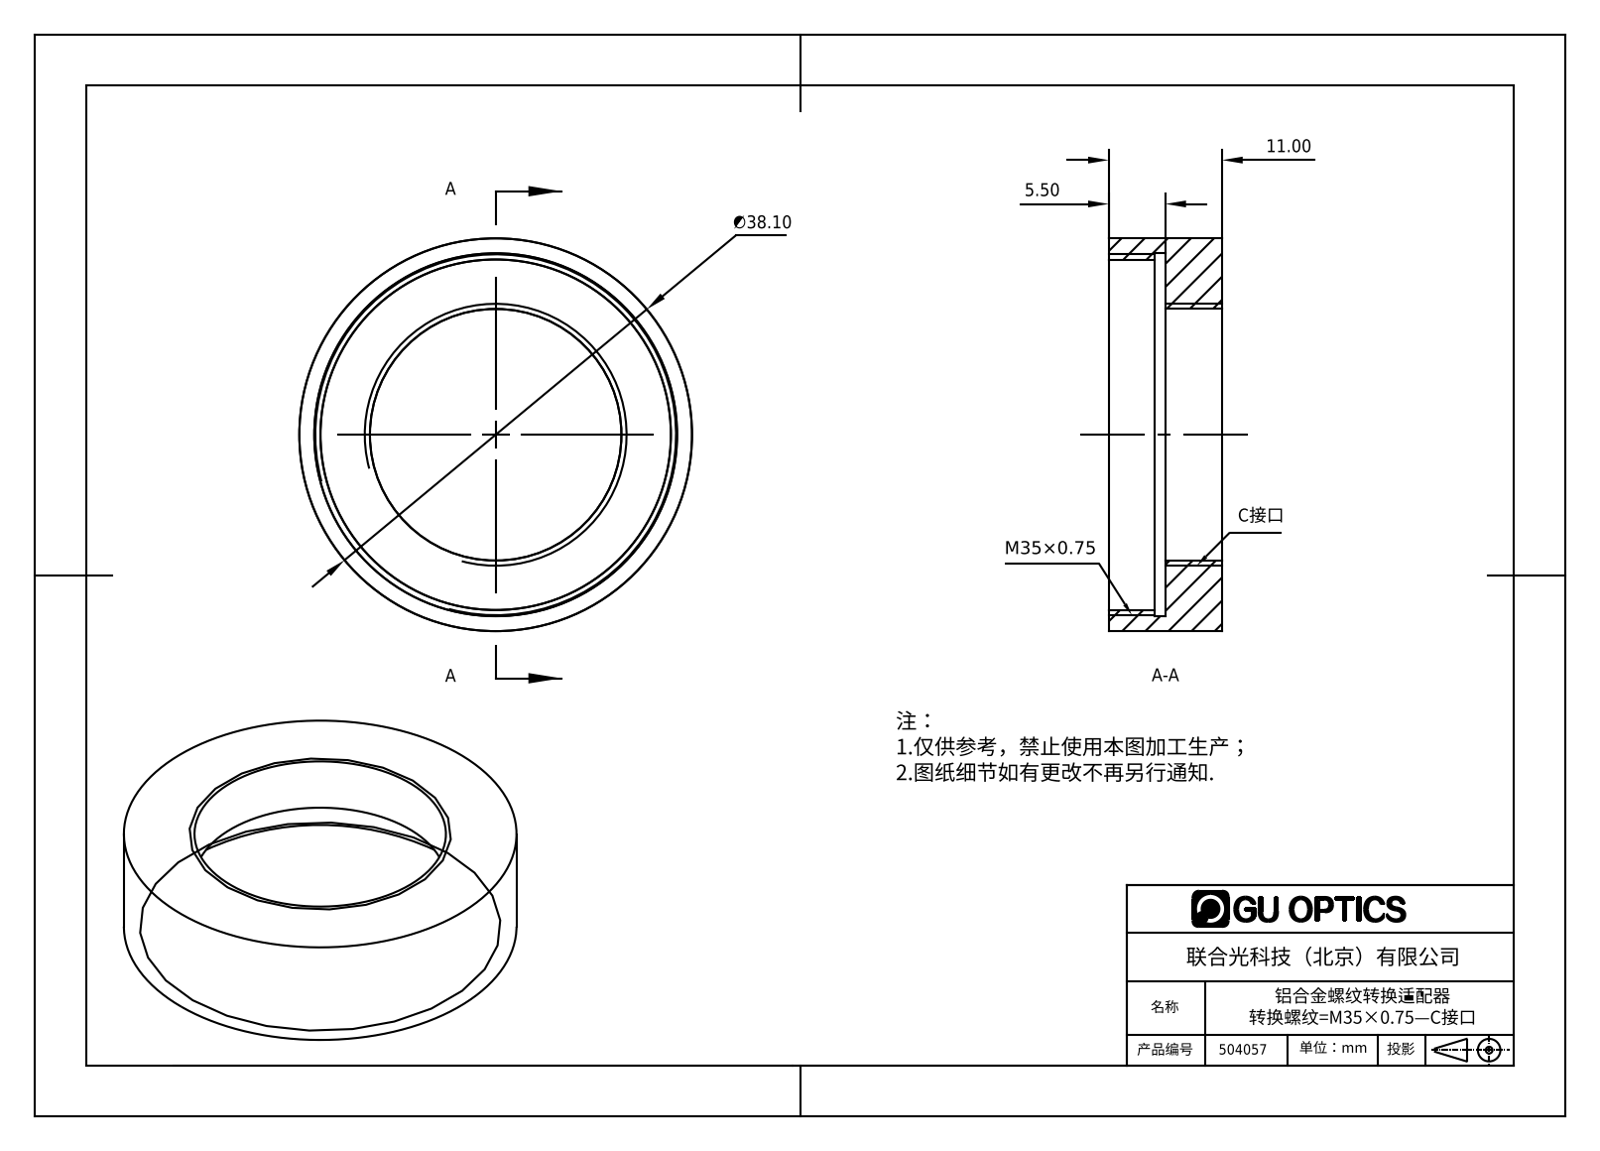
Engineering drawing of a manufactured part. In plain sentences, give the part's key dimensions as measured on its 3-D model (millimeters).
The part is named "504057". Its 3-D file was written by "SolidWorks 2016 (AUTOMOTIVE_DESIGN)". It is 1 solid with 12 faces: 4 planar, 8 cylindrical and 0 other. Overall it measures 38.1 by 38.1 by 11 millimeters. Its volume is 4 910 cubic millimeters and its surface area 3 805 square millimeters. Round holes: 1 of diameter 24.4, 1 of diameter 34, 1 of diameter 35.2. Round bosses or shafts: 1 of diameter 38.1. The main face-to-face distances are 5.5, 11, 4.5, 1, 6.5.
